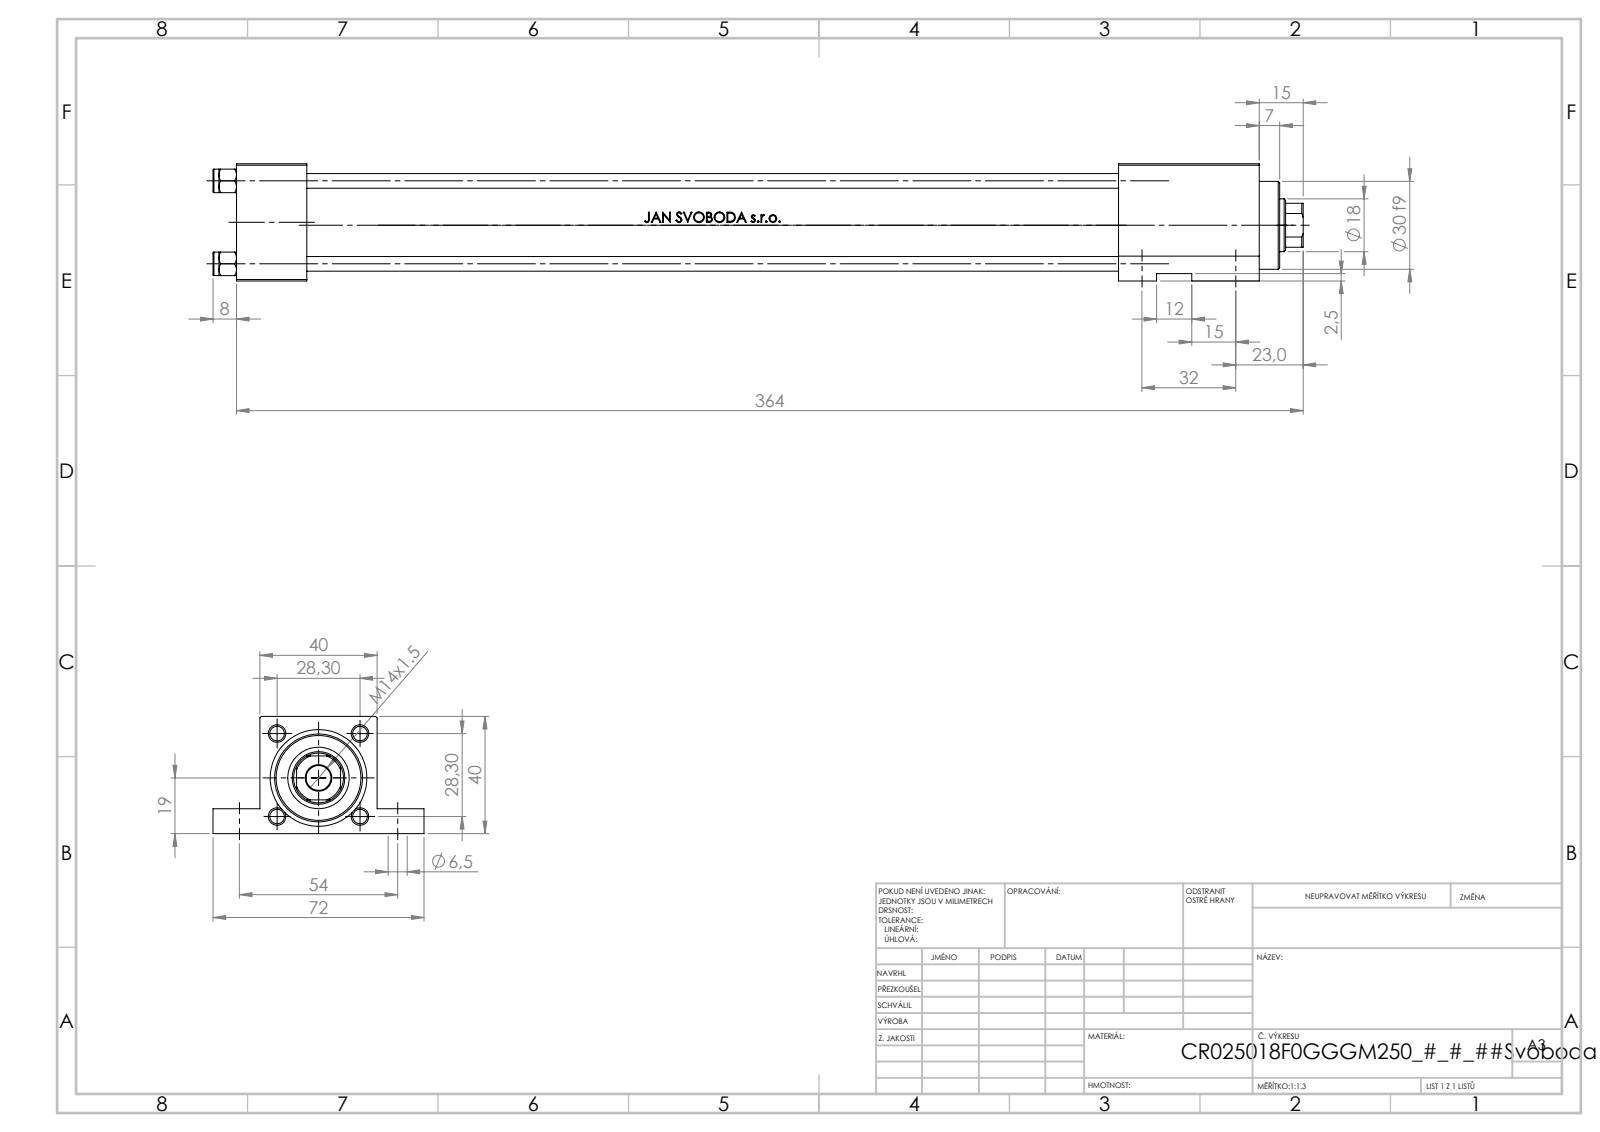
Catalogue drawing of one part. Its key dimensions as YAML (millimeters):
part_name: "V215_VC_A; V215CR_VCP_F; NUT_M5_F; V215CR_F_TYCINKA (+1 more)"
step_written_by: "SolidWorks 2019 (CONFIG_CONTROL_DESIGN)"
units: millimeters
bodies: {solids: 11, faces: 1100, planar: 436, cylindrical: 124, other: 540}
overall_size: [372, 72, 40]
volume: 296931
surface_area: 128845
round_holes:
  - {diameter: 5, count: 4}
  - {diameter: 6.5, count: 4}
  - {diameter: 20, count: 3}
  - {diameter: 7, count: 2}
  - {diameter: 13.16, count: 2}
  - {diameter: 8.5, count: 1}
  - {diameter: 18, count: 1}
  - {diameter: 21, count: 1}
  - {diameter: 25, count: 1}
  - {diameter: 30, count: 1}
round_bosses_or_shafts:
  - {diameter: 8, count: 4}
  - {diameter: 31, count: 1}
partial_cylinders:
  - {radius: 8.5, count: 1}
face_to_face_distances: [40, 24, 8.5, 31.5, 301, 277, 48, 6, 349, 325]
hole_center_spacings: [28.3, 19.32, 20.73, 27.46, 32, 38.18, 40.02, 54]
